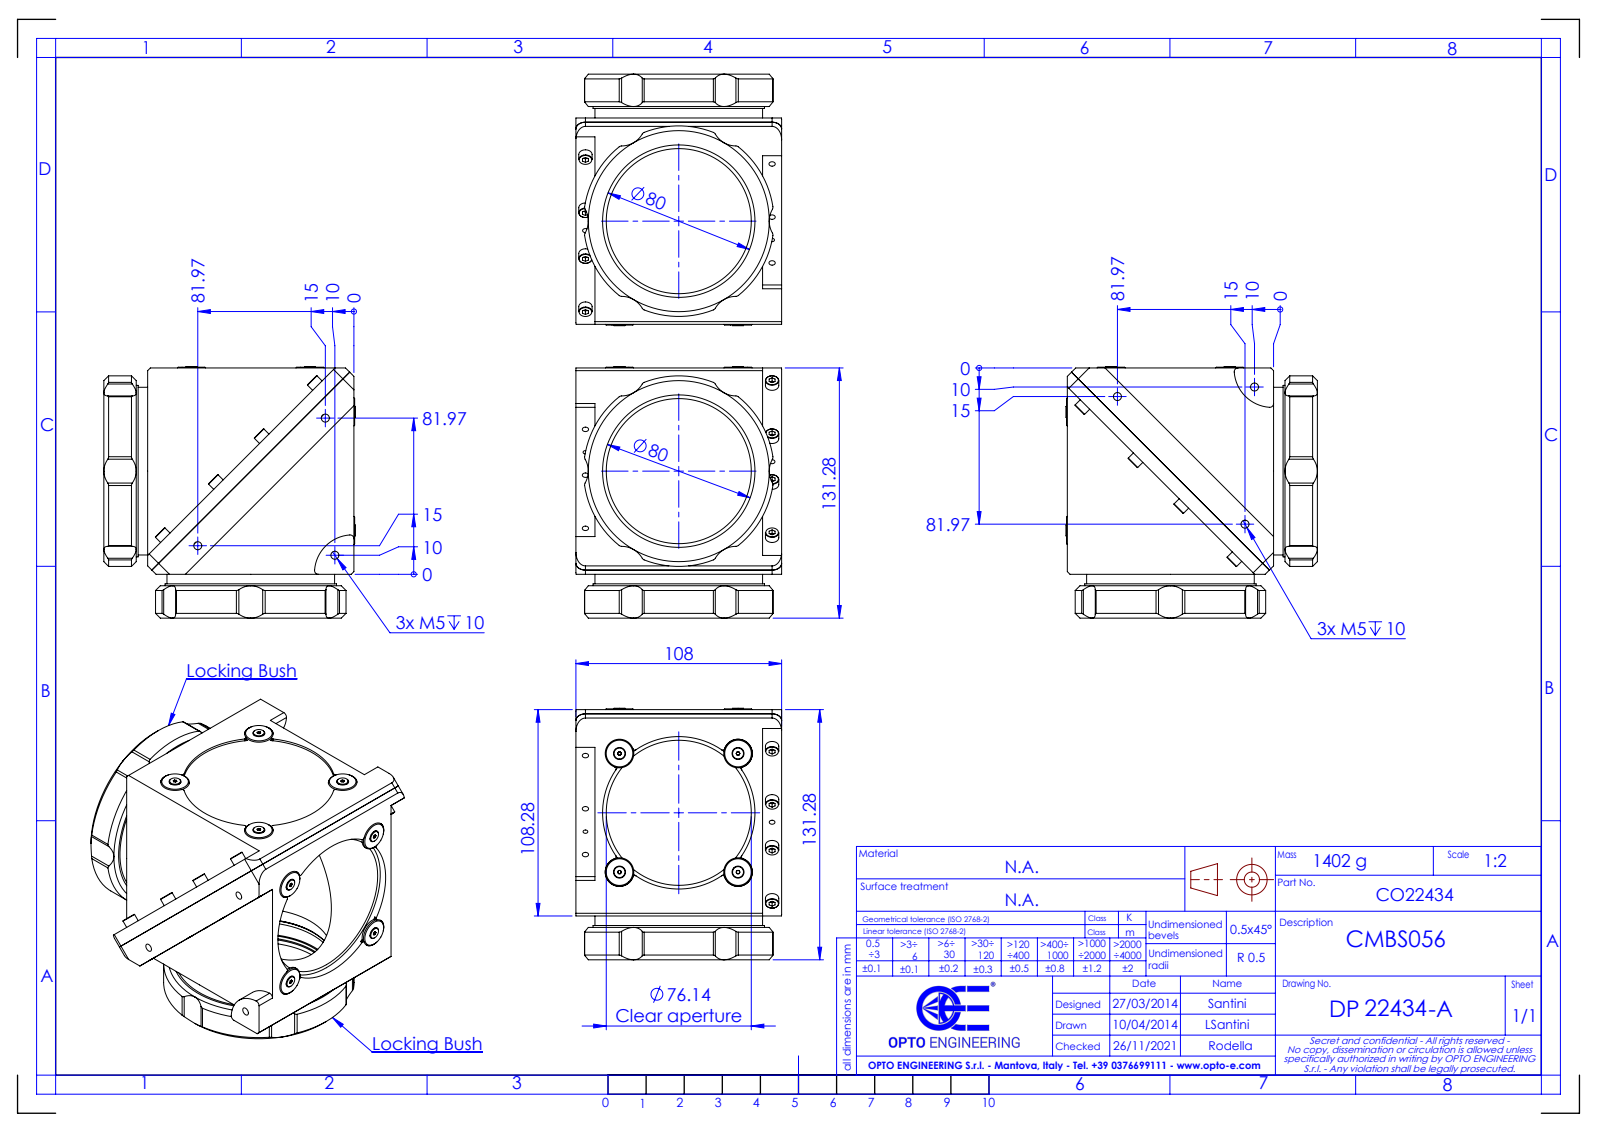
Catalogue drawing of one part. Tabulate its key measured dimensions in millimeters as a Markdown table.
| quantity | value |
| --- | --- |
| part name | DP22434 -A_CMBS056 |
| STEP written by | SolidWorks 2021 (CONFIG_CONTROL_DESIGN) |
| units | millimeters |
| bodies | 0 solids, 523 faces (166 planar, 241 cylindrical, 116 other) |
| overall size | 132.01 × 132.01 × 108 |
| round holes (diameter × count) | 3.3 × 8, 4.2 × 6, 15 × 3, 2.5 × 2, 3 × 2, 76.14 × 2, 80 × 2, 80.6 × 2, 82.2 × 2, 84 × 2, 88 × 2, 90 × 1 |
| round bosses / shafts (diameter × count) | 7 × 8, 5.75 × 8, 15 × 5, 90 × 1 |
| partial cylindrical surfaces (radius × count) | 2 × 28, 1 × 16, 12.5 × 12, 5 × 4, 20 × 2, 50 × 2 |
| main face-to-face distances | 2, 88, 108.28, 10, 98, 3, 7, 1, 4, 104.28 |
| hole center spacings | 98, 17, 39.44, 56.44, 72.14, 73.44, 84.86, 99.46 |
